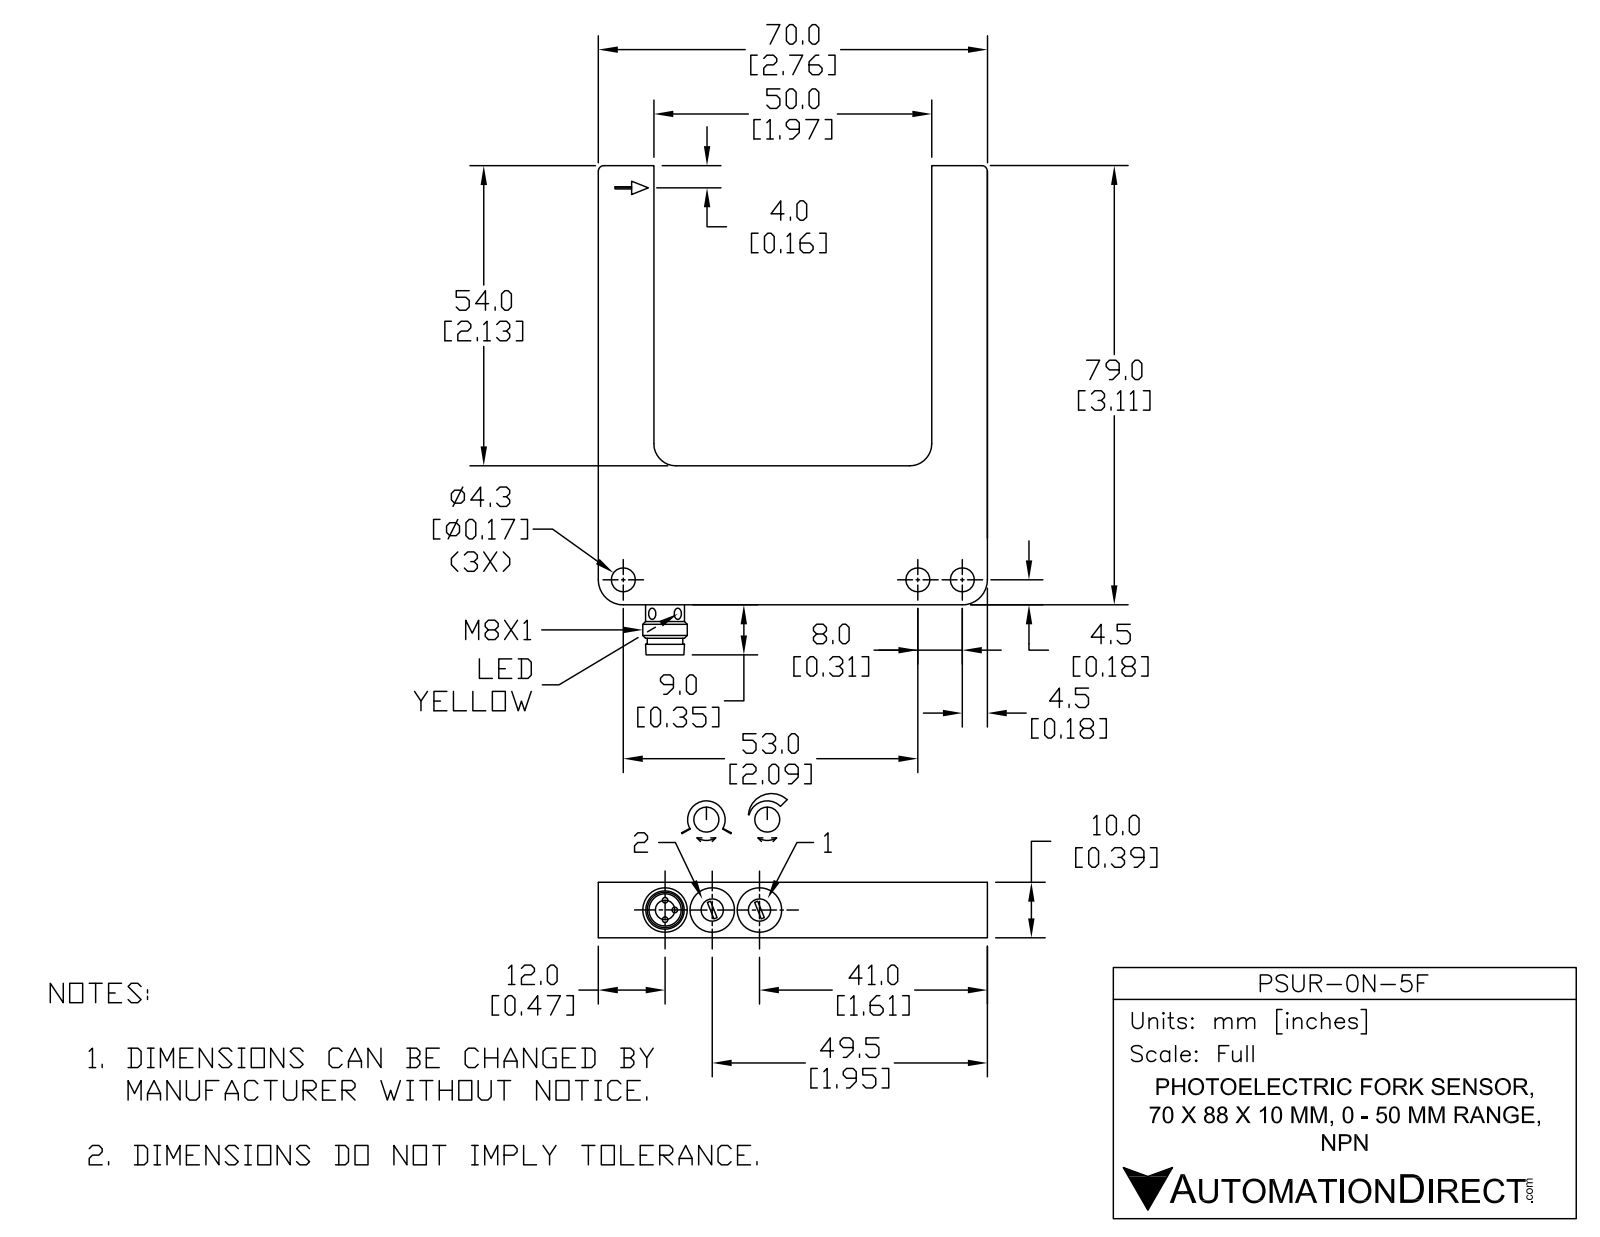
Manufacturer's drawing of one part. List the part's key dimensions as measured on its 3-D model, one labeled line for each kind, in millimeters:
Part name (STEP PRODUCT): PSUR-0N-5F
STEP written by: SolidWorks 2019 (AUTOMOTIVE_DESIGN)
Units: millimetres
Bodies: 1 solid, 95 faces (35 planar, 48 cylindrical, 12 other)
Overall size (bounding box): 88 × 70 × 10
Volume: 28 050 mm³ · Surface area: 10 320 mm²
Round holes (diameter × count): ⌀4.3 ×3, ⌀2 ×2, ⌀4 ×2, ⌀8 ×2, ⌀5.8 ×1
Round bosses / shafts (diameter × count): ⌀1 ×3, ⌀8 ×1, ⌀6.8 ×1
Partial cylindrical surfaces — rounded edges, fillets, slot ends (radius × count): R0.5 ×2, R1 ×2, R1.6 ×2, R4 ×2, R4.5 ×2
Main face-to-face distances: 10, 60, 70, 50, 25, 54, 79, 78.9, 24.9, 4
Hole centre spacings: 8.5, 8, 17, 53, 61
